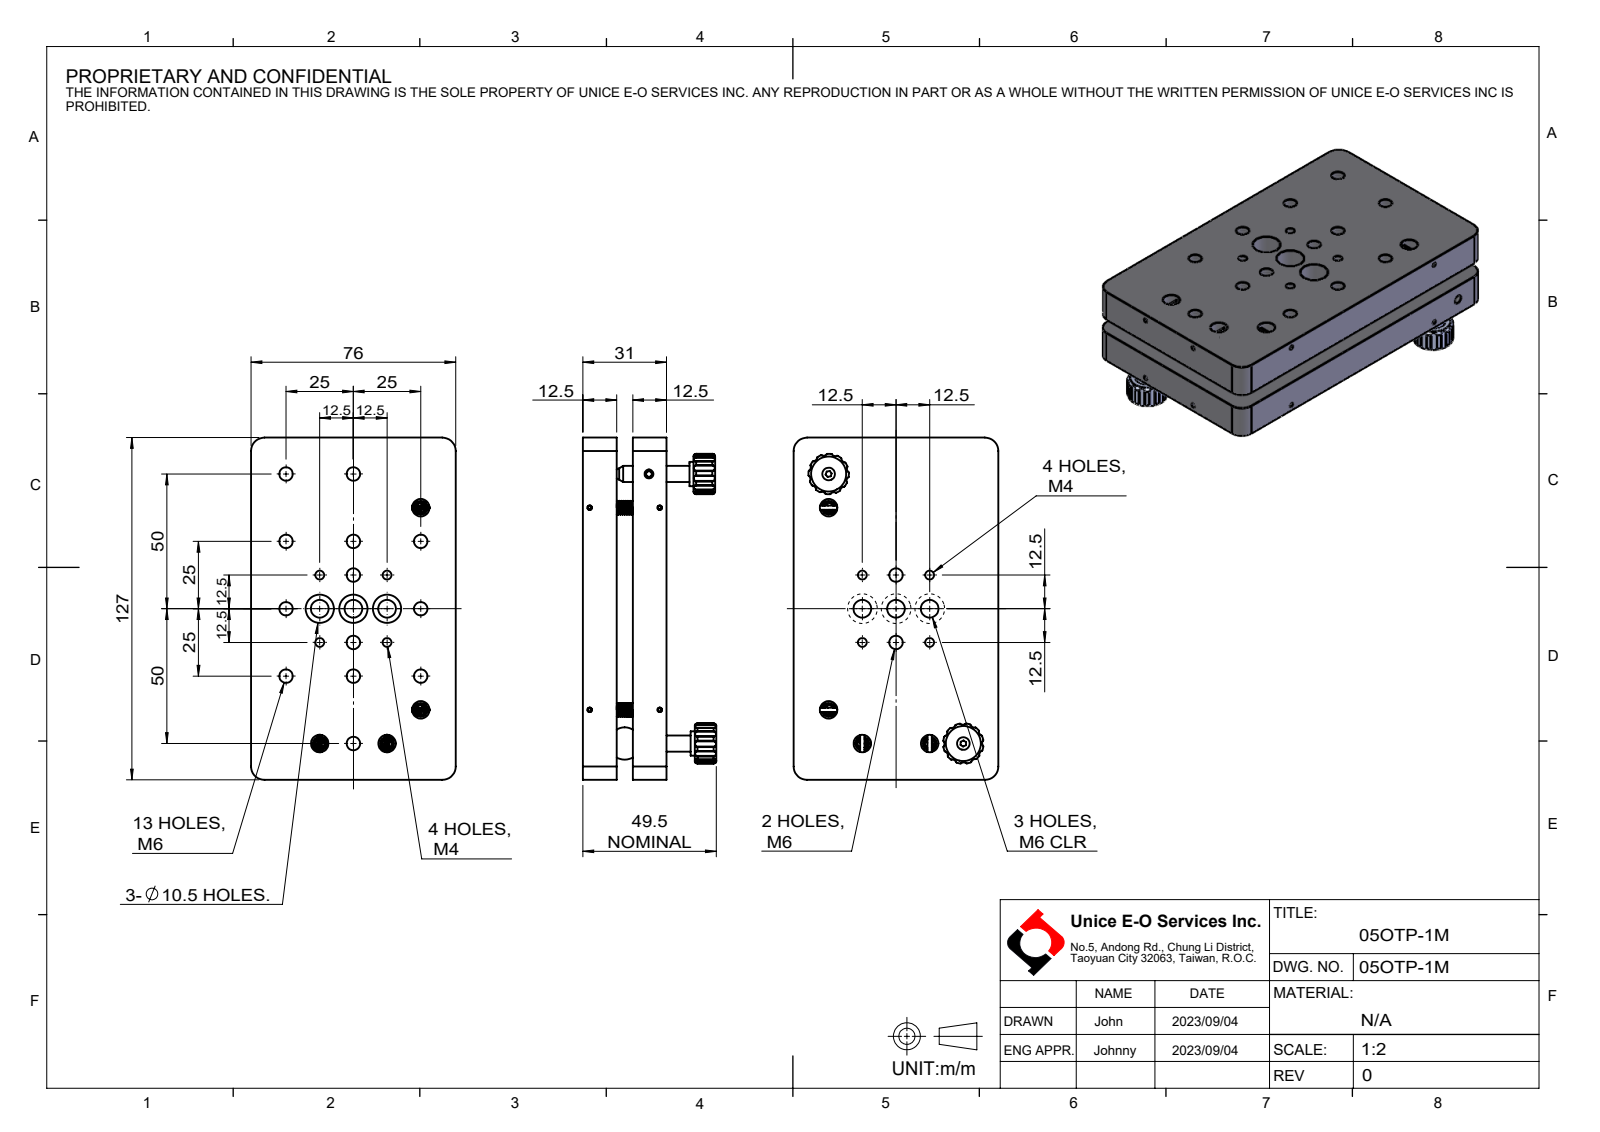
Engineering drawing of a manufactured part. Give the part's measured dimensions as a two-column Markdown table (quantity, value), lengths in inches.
| quantity | value |
| --- | --- |
| part name | 05OTP-1M |
| STEP written by | SolidWorks 2022 (CONFIG_CONTROL_DESIGN) |
| units | inches |
| bodies | 28 solids, 415 faces (129 planar, 225 cylindrical, 61 other) |
| overall size | 5 × 2.992 × 1.949 |
| volume | 14.13 in³ |
| surface area | 100.1 in² |
| round holes (diameter × count) | 0.197 × 13, 0.047 × 8, 0.067 × 8, 0.13 × 6, 0.256 × 4, 0.26 × 3, 0.413 × 3, 0.433 × 3, 0.157 × 2, 0.185 × 2, 0.204 × 2, 0.226 × 2 |
| round bosses / shafts (diameter × count) | 0.031 × 16, 0.063 × 8, 0.372 × 2, 0.354 × 2, 0.236 × 2, 0.157 × 2, 0.059 × 2 |
| partial cylindrical surfaces (radius × count) | 0.012 × 48, 0.059 × 25, 0.03 × 4, 0.197 × 4, 0.295 × 2 |
| main face-to-face distances | 0.728, 0.492, 1.22, 0.236, 2.992, 5, 0.276, 0.217, 0.018, 0.512 |
| hole center spacings | 1.1, 0.984, 1.556, 0.492, 2.201, 0.696, 1.392, 1.774 |
